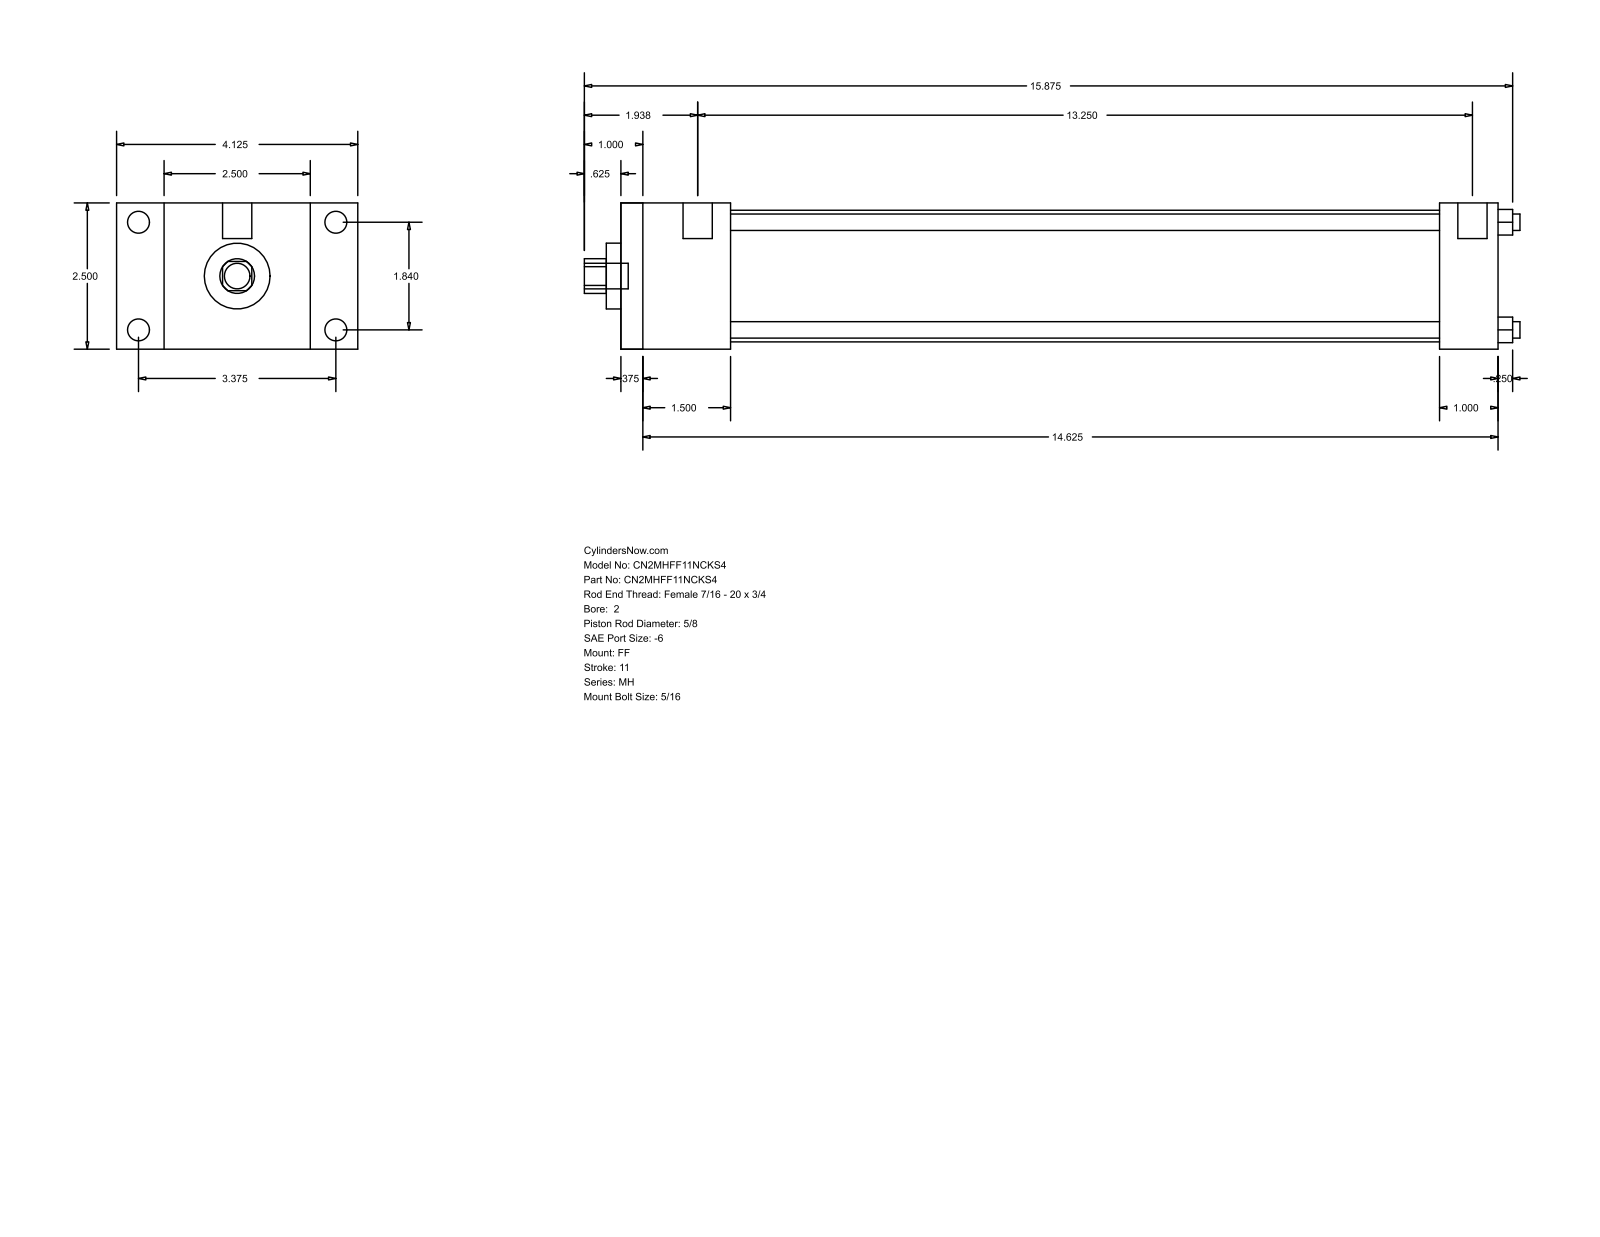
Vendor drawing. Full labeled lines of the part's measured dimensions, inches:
Part name (STEP PRODUCT): MH_FF__0200_0.625
STEP written by: GSSL Pune (CONFIG_CONTROL_DESIGN)
Units: inches
Bodies: 0 solids, 92 faces (64 planar, 28 cylindrical, 0 other)
Overall size (bounding box): 16 × 4.125 × 2.5
Round holes (diameter × count): ⌀0.281 ×4, ⌀0.625 ×1, ⌀1.125 ×1, ⌀2.25 ×1
Round bosses / shafts (diameter × count): ⌀0.375 ×4, ⌀0.219 ×4, ⌀0.5 ×2, ⌀0.437 ×1
Partial cylindrical surfaces — rounded edges, fillets, slot ends (radius × count): R0.297 ×1
Main face-to-face distances: 2.5, 15, 0.375, 14.625, 1, 1.5, 1.875, 14, 13.625, 12.125
Hole centre spacings: 1.301, 1.84, 2.602
